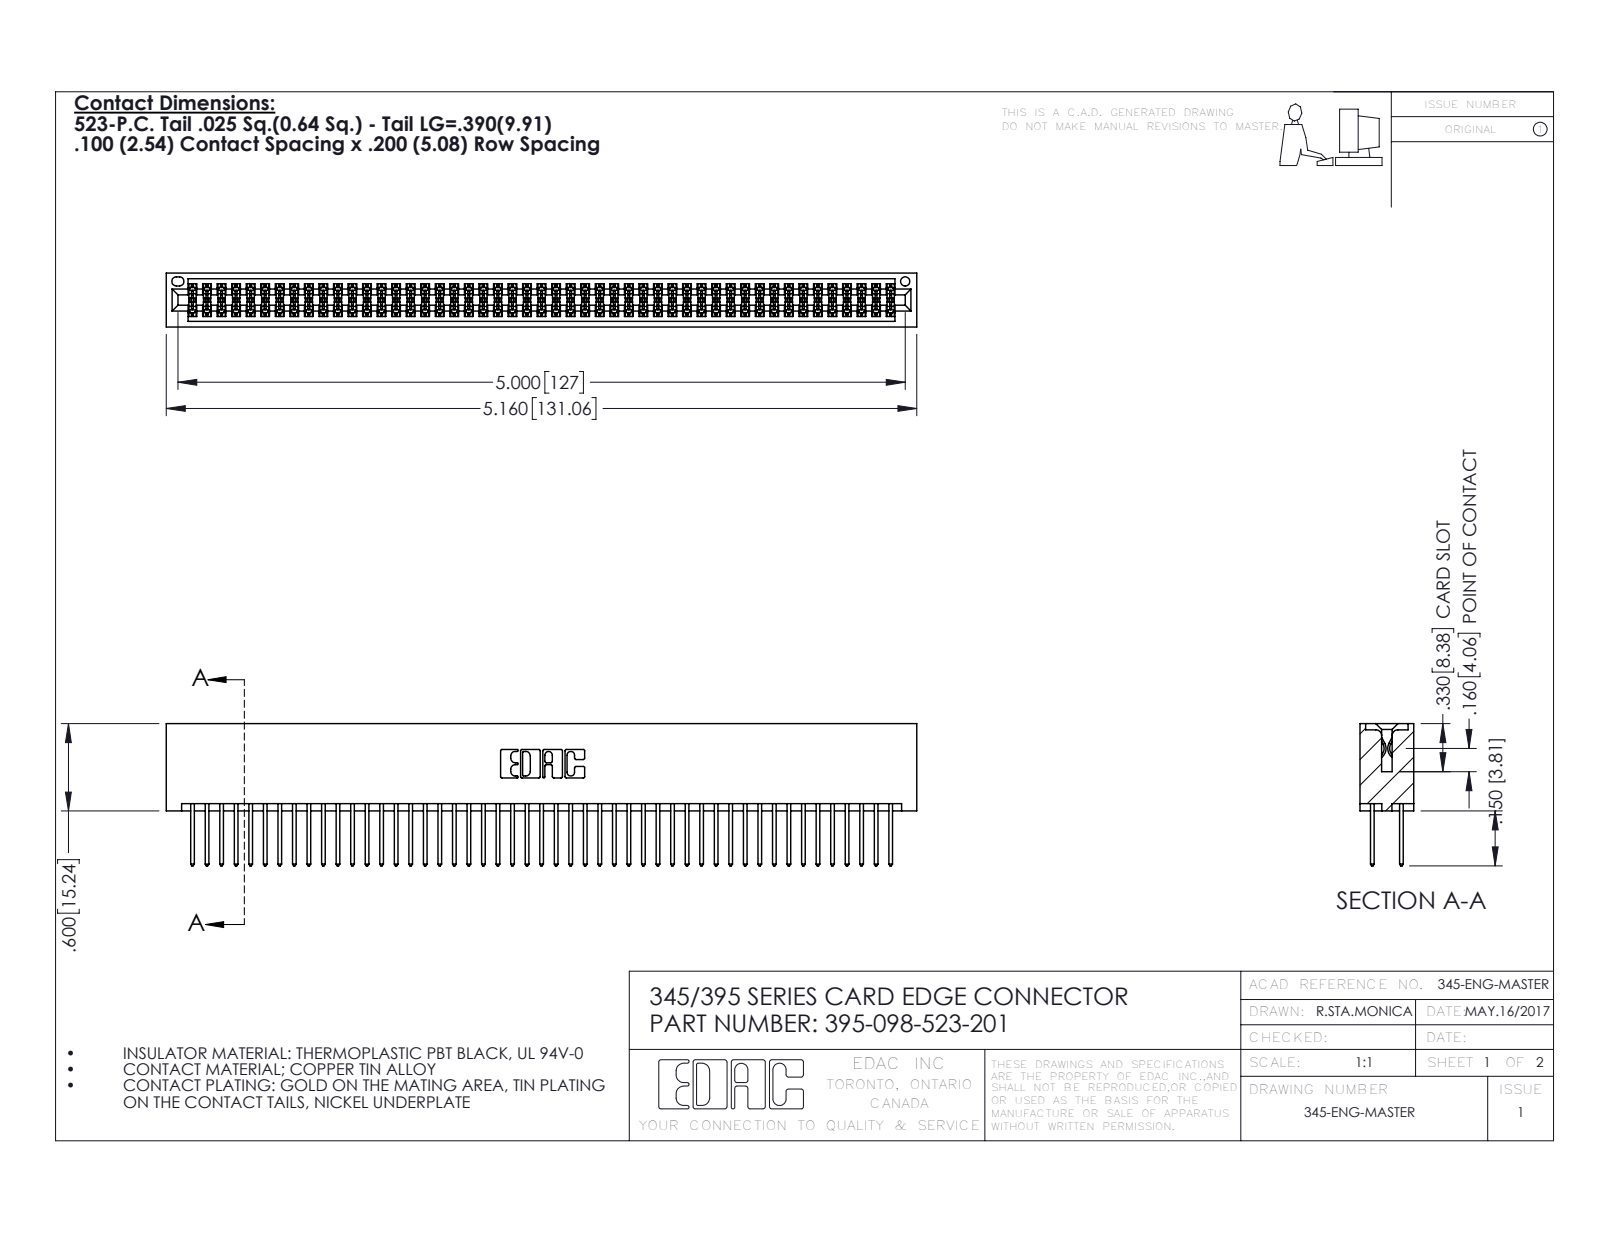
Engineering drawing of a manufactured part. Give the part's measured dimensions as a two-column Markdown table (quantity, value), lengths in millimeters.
| quantity | value |
| --- | --- |
| part name | 345 Part_No Mounting Lugs; 345-292-001_345-293-123; 395-098-523-201 |
| STEP written by | SolidWorks 2016 (CONFIG_CONTROL_DESIGN) |
| units | millimeters |
| bodies | 99 solids, 5018 faces (3310 planar, 1708 cylindrical, 0 other) |
| overall size | 131.1 × 24.8 × 9.4 |
| volume | 13 600 mm³ |
| surface area | 21 460 mm² |
| round holes (diameter × count) | 1.6 × 1 |
| partial cylindrical surfaces (radius × count) | 0.2 × 147, 0.3 × 98, 0.3 × 22, 0.2 × 6, 0.8 × 6, 0.7 × 3, 0.4 × 2, 0.5 × 2 |
| main face-to-face distances | 7.6, 1.8, 5.1, 2.5, 6.9, 0.6, 9.4, 5.7, 4.4, 3.8 |
